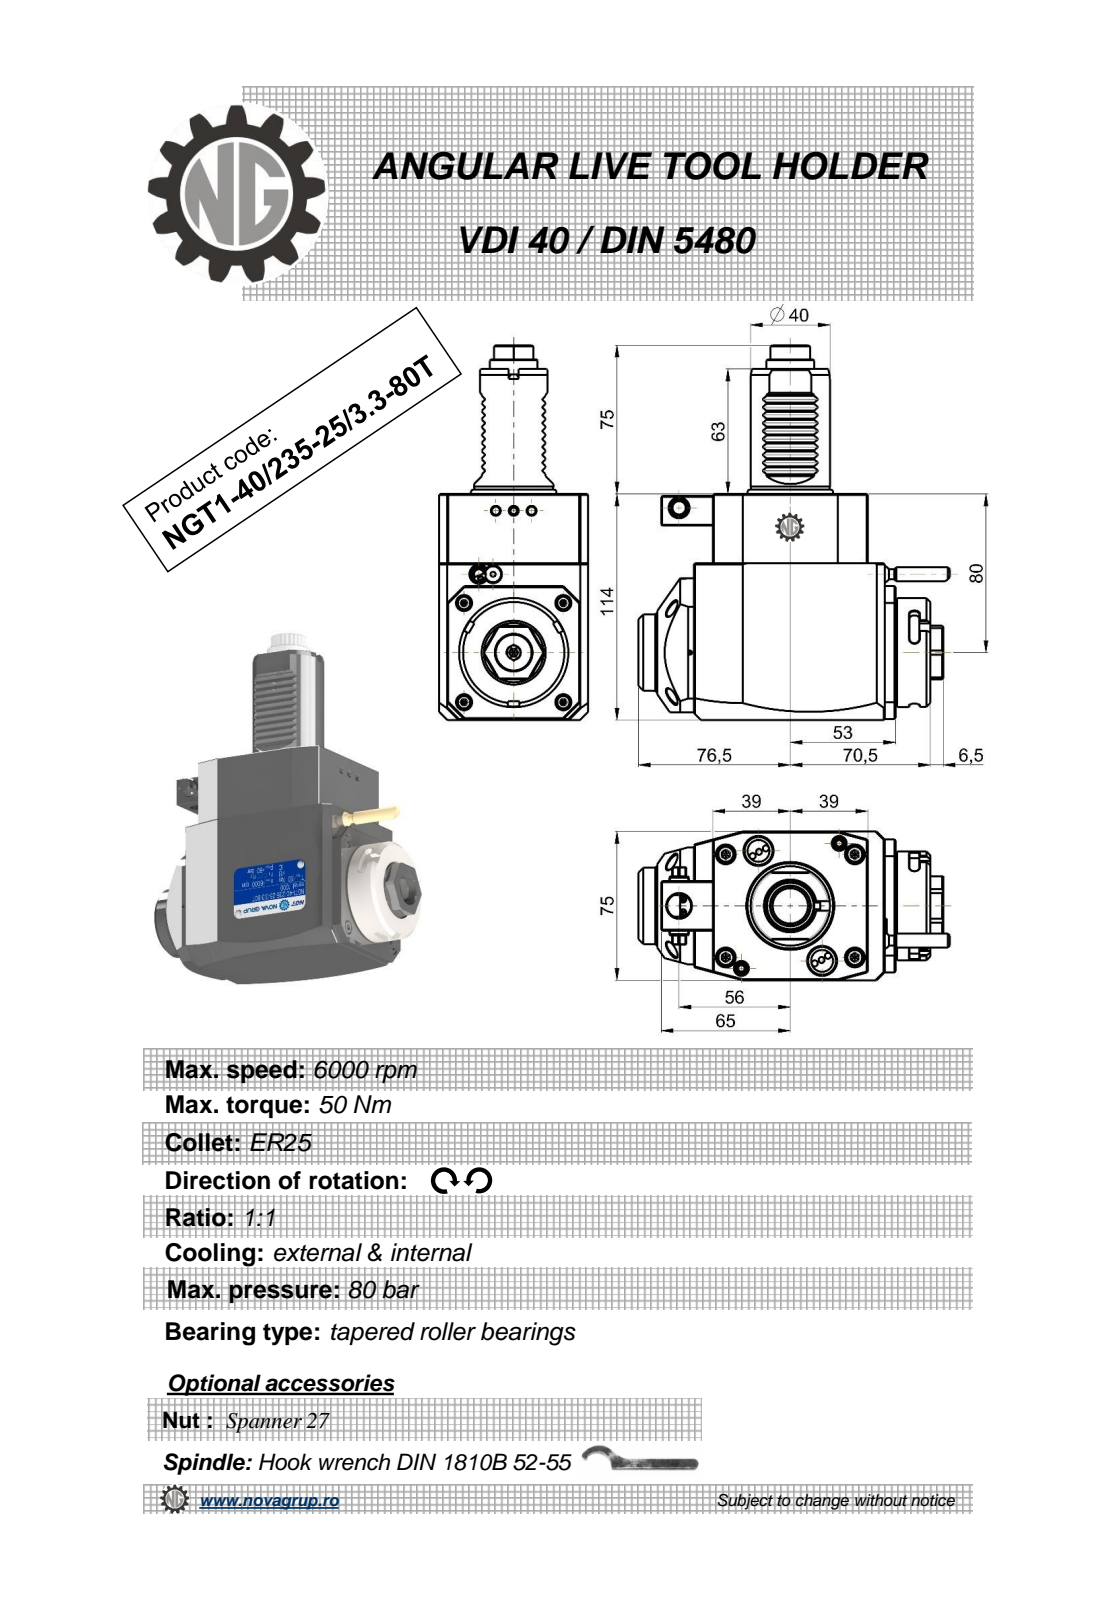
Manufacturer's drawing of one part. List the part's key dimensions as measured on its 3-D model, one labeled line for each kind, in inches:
Part name (STEP PRODUCT): NGT1_40_235_25_3_3_80T
STEP written by: PRO/ENGINEER BY PARAMETRIC TECHNOLOGY CORPORATION, 2010280 (CONFIG_CONTROL_DESIGN)
Units: inches
Bodies: 1 solid, 512 faces (222 planar, 190 cylindrical, 100 other)
Overall size (bounding box): 7.441 × 6.174 × 2.953
Volume: 58.97 in³ · Surface area: 112 in²
Round holes (diameter × count): ⌀0.098 ×1, ⌀0.118 ×1, ⌀0.374 ×1, ⌀0.472 ×1, ⌀0.709 ×1
Round bosses / shafts (diameter × count): ⌀0.315 ×2, ⌀2.165 ×1, ⌀1.89 ×1, ⌀1.575 ×1, ⌀1.516 ×1, ⌀0.945 ×1, ⌀0.394 ×1, ⌀0.276 ×1
Partial cylindrical surfaces — rounded edges, fillets, slot ends (radius × count): R0.082 ×48, R0.012 ×20, R0.098 ×6, R0.591 ×2, R7.087 ×2, R0.152 ×1, R0.167 ×1, R0.357 ×1
Main face-to-face distances: 2.953, 4.488, 0.551, 0.689, 4.311, 3.071, 3.622, 1.24, 3.11, 1.378
Hole centre spacings: 1.436, 1.701, 2.815
